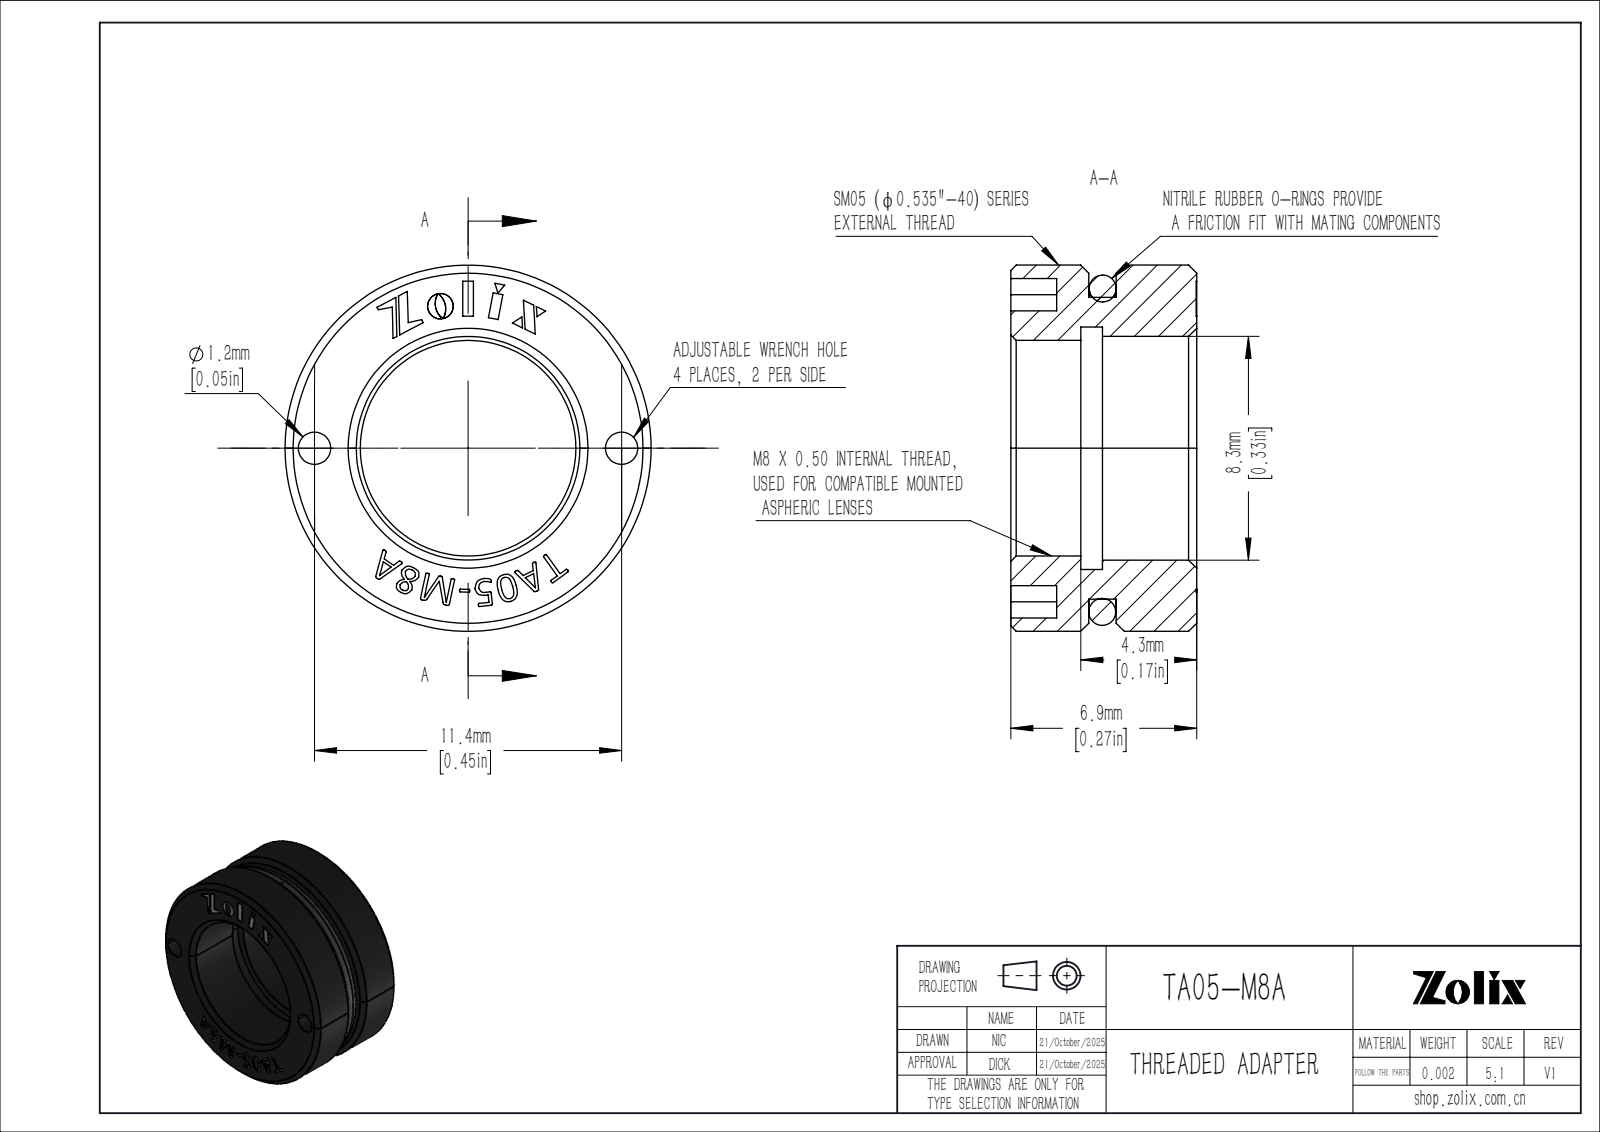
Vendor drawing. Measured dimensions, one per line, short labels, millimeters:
name: TA05-M8A
written by: SolidWorks 2020 (CONFIG_CONTROL_DESIGN)
unit: mm
bodies: 2 solids, 328 faces (214 planar, 20 cylindrical, 94 other)
size: 13.59 × 13.59 × 6.9
volume: 596 mm³; area: 879 mm²
holes: 4× ⌀1.2, 1× ⌀8, 1× ⌀8.3, 1× ⌀9
bosses: 1× ⌀13.59, 1× ⌀11.2
face distances: 6.9, 2.89, 4.01, 3.91, 1.02, 2.99, 0.51, 2.6, 1.31, 4.3
hole spacings: 5.7, 8.06, 11.4
